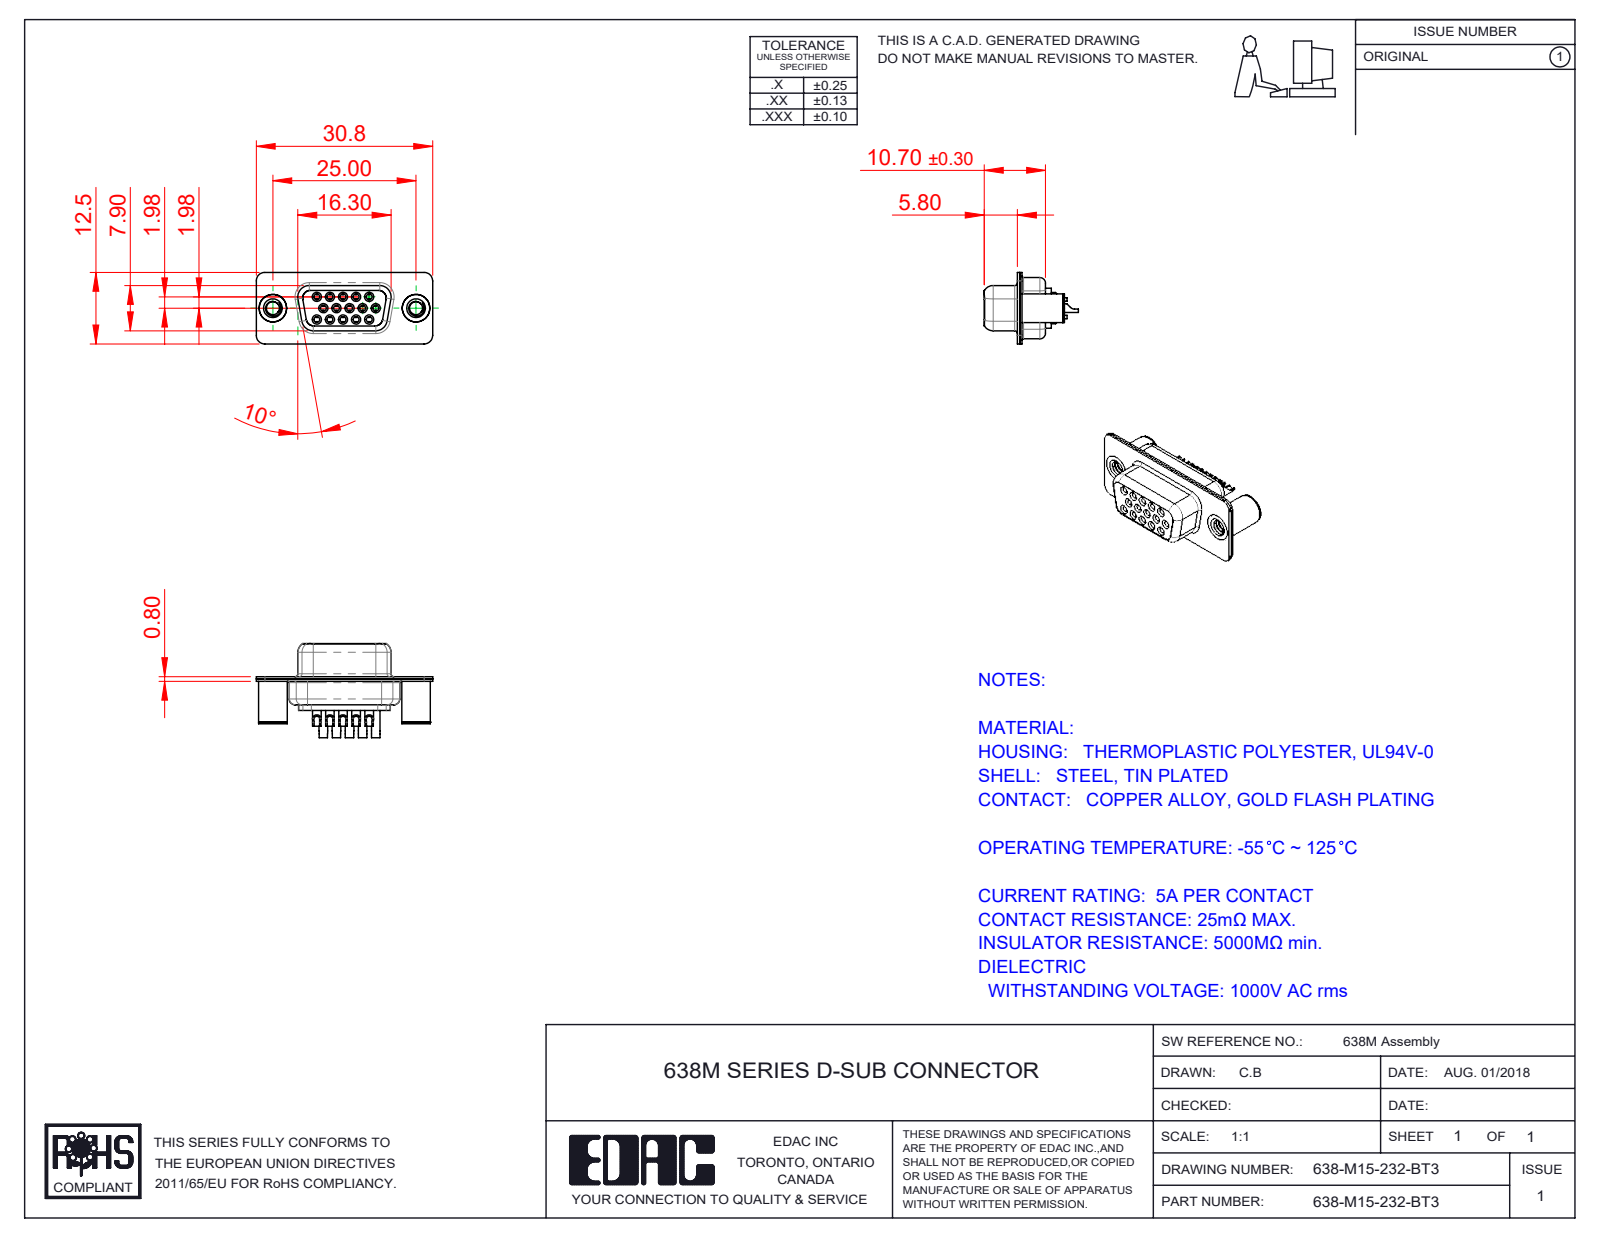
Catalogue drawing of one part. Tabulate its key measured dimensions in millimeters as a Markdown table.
| quantity | value |
| --- | --- |
| part name | 638M Housing_15 Contacts; 638M Shell Front_15 Contacts; 638M Contact Row 1_32; 638M 4-40 Threaded Board Spacer (+4 more) |
| STEP written by | SolidWorks 2020 (CONFIG_CONTROL_DESIGN) |
| units | millimeters |
| bodies | 20 solids, 1138 faces (322 planar, 476 cylindrical, 340 other) |
| overall size | 30.8 × 16.45 × 12.5 |
| volume | 1 782 mm³ |
| surface area | 5 691 mm² |
| round holes (diameter × count) | 1 × 16, 1.1 × 15, 1.7 × 15, 1.8 × 15, 2 × 15, 2.26 × 2, 3.26 × 2, 4 × 2, 4.8 × 2 |
| round bosses / shafts (diameter × count) | 2.2 × 15, 1.6 × 15, 1.5 × 15, 5 × 2, 4.9 × 2 |
| partial cylindrical surfaces (radius × count) | 1.5 × 16, 2 × 12, 1.35 × 8, 1.6 × 8, 1 × 7, 0.25 × 4, 0.5 × 4, 0.6 × 4 |
| main face-to-face distances | 0.4, 1.4, 0.45, 8.45, 0.8, 8.9, 1, 1.8, 6.2, 7.05 |
| hole center spacings | 2.28, 3.96, 2.29, 4.57, 6.05, 6.04, 6.86, 7.92 |
